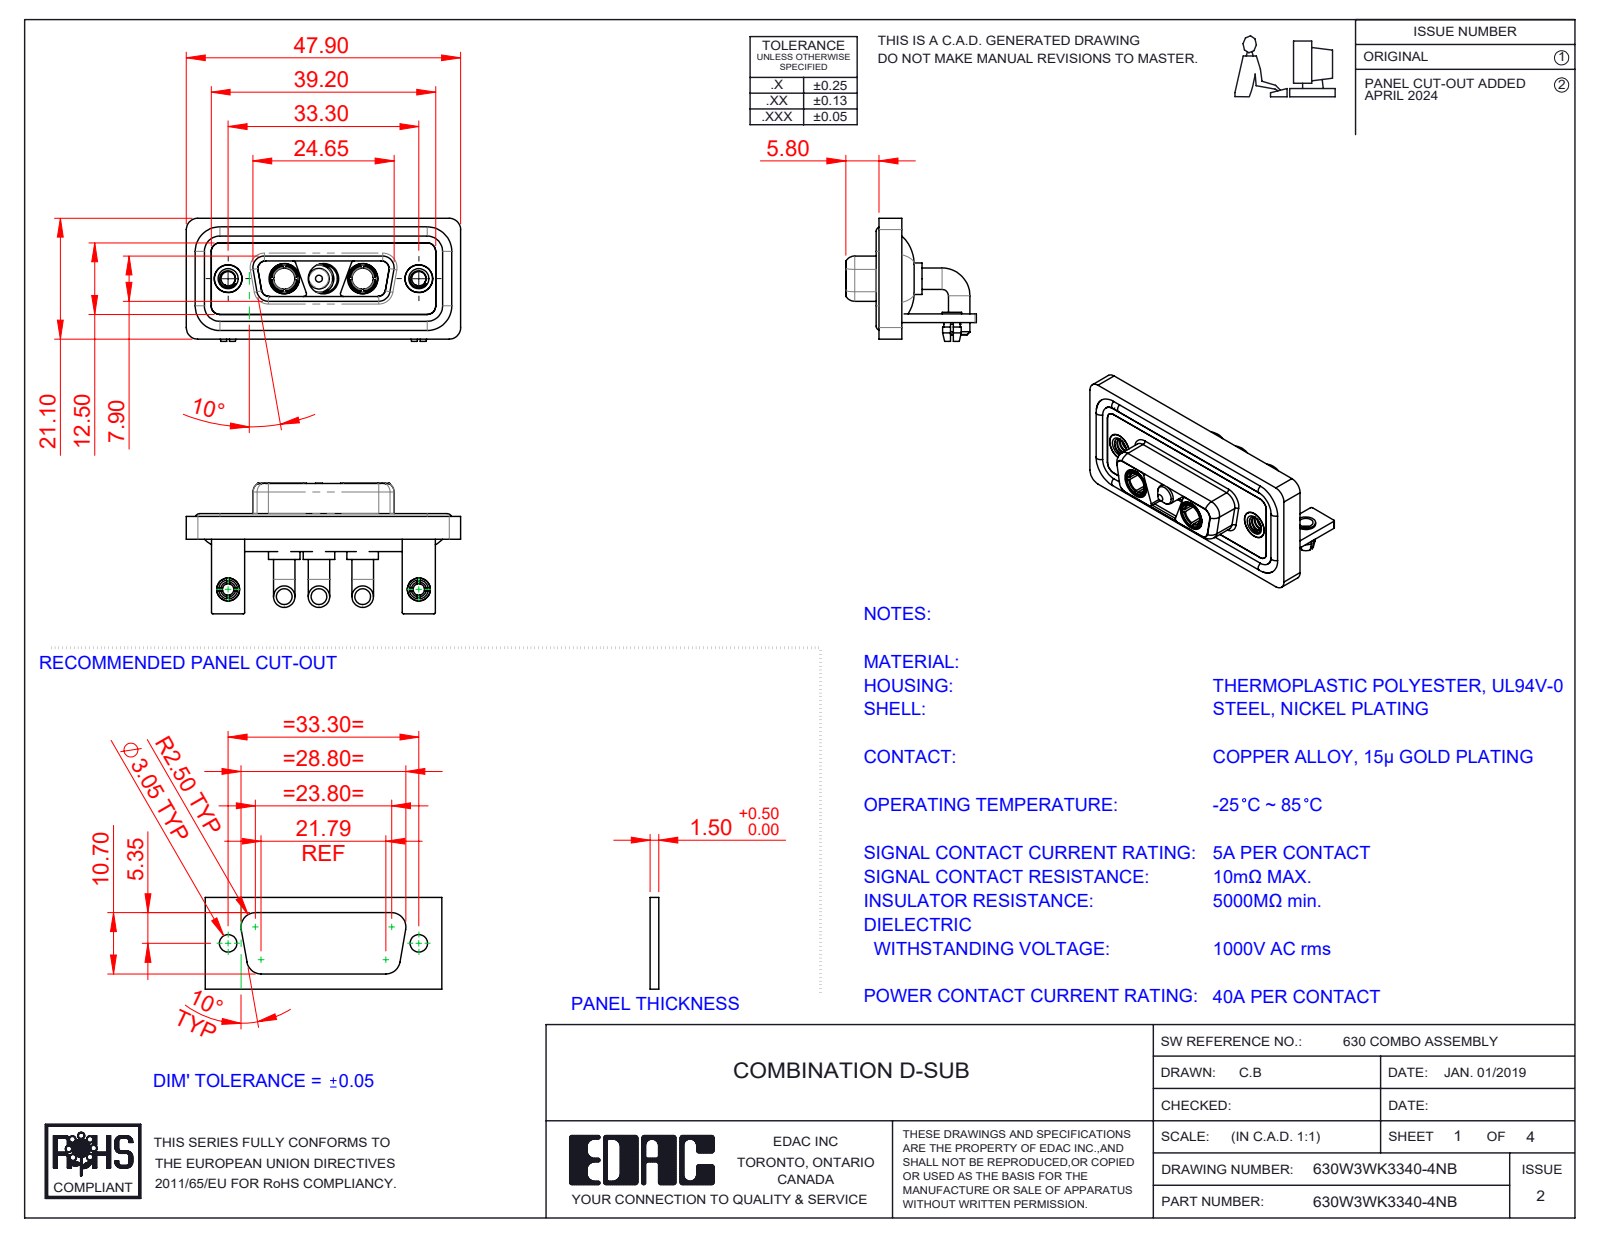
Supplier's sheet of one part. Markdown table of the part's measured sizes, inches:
| quantity | value |
| --- | --- |
| part name | 630Combo Shell Rear_15 Contacts; Power Socket_40A RA; 630Combo Threaded Rivet_A; 630Combo Shell Front_15 Contacts (+6 more) |
| STEP written by | SolidWorks 2023 (CONFIG_CONTROL_DESIGN) |
| units | inches |
| bodies | 17 solids, 729 faces (246 planar, 318 cylindrical, 165 other) |
| overall size | 1.886 × 0.898 × 0.846 |
| volume | 0.406 in³ |
| surface area | 16.77 in² |
| round holes (diameter × count) | 0.191 × 5, 0.098 × 4, 0.209 × 3, 0.079 × 2, 0.126 × 2, 0.146 × 2, 0.157 × 2, 0.159 × 2, 0.197 × 2 |
| round bosses / shafts (diameter × count) | 0.148 × 6, 0.063 × 4, 0.217 × 3, 0.205 × 3, 0.187 × 3, 0.195 × 2, 0.195 × 2, 0.189 × 2 |
| partial cylindrical surfaces (radius × count) | 0.079 × 21, 0.059 × 18, 0.01 × 16, 0.053 × 12, 0.02 × 9, 0.063 × 8, 0.024 × 4, 0.026 × 4 |
| main face-to-face distances | 0.016, 0.114, 0.059, 0.146, 0.071, 0.043, 0.161, 0.063, 0.098, 0.055 |
| hole center spacings | 0.27, 0.386, 0.656, 0.925, 1.311, 0.539 |
